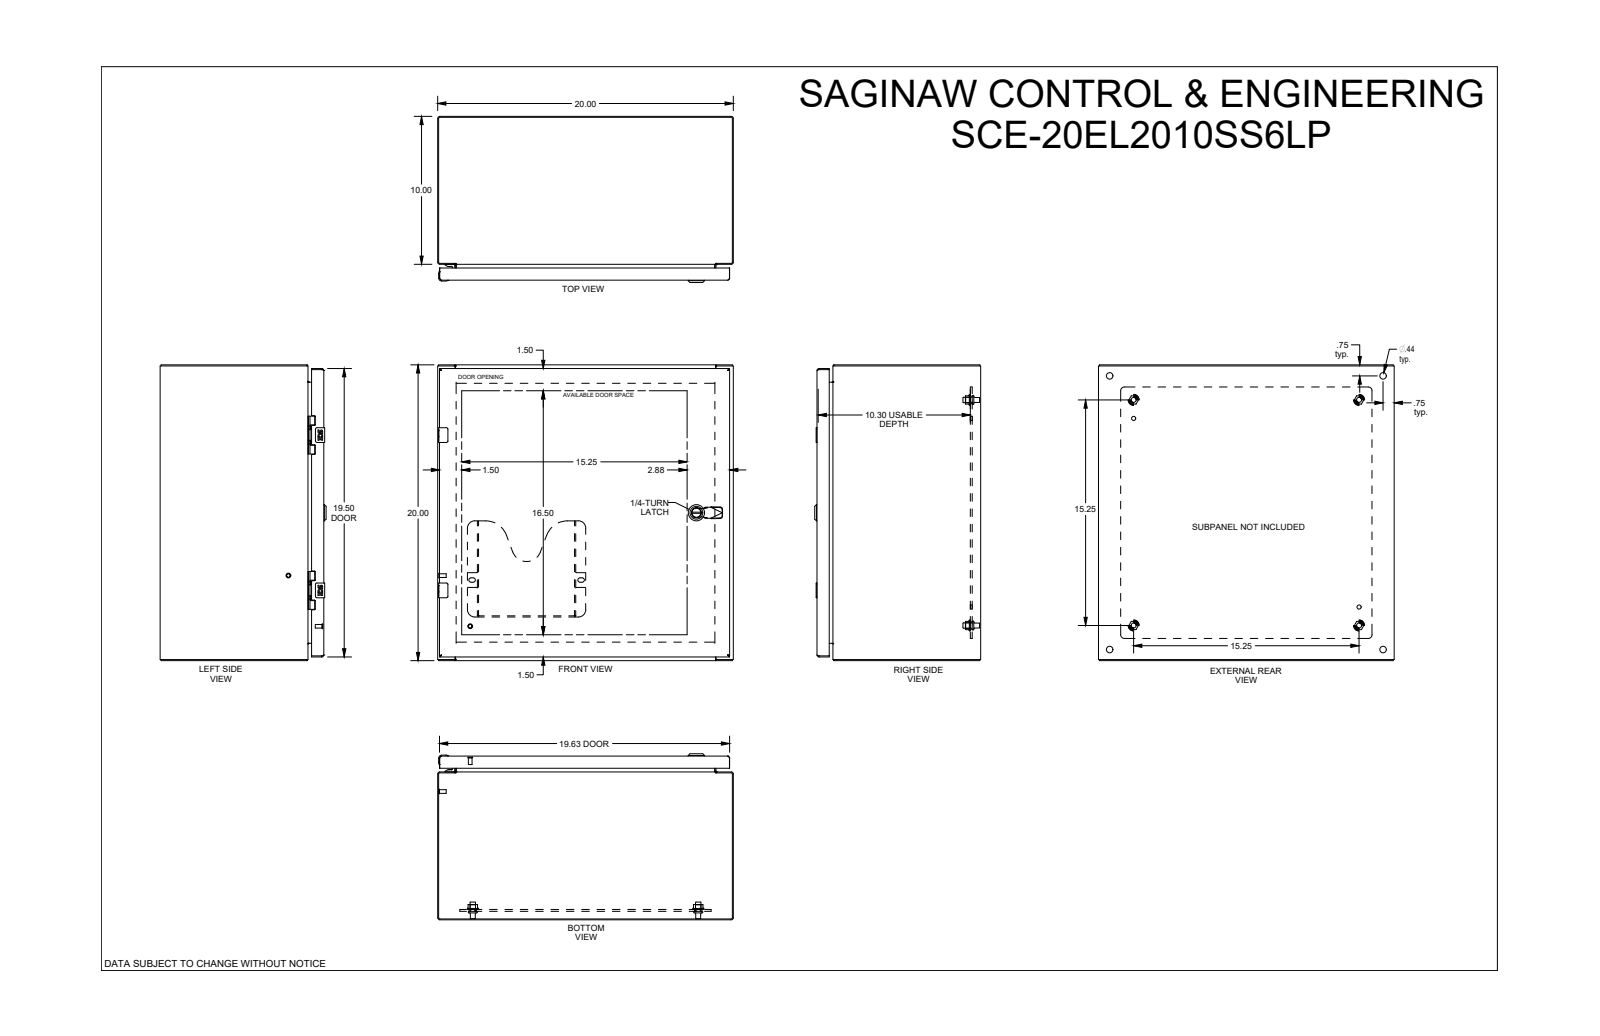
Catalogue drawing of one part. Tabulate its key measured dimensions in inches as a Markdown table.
| quantity | value |
| --- | --- |
| part name | SCE-20EL2010LP |
| STEP written by | SolidWorks 2021 (AUTOMOTIVE_DESIGN) |
| units | inches |
| bodies | 24 solids, 1217 faces (544 planar, 474 cylindrical, 199 other) |
| overall size | 20 × 20 × 11.935 |
| volume | 182.7 in³ |
| surface area | 4 462 in² |
| round holes (diameter × count) | 0.172 × 4, 0.205 × 4, 0.244 × 4, 0.375 × 4, 0.437 × 4, 0.5 × 4, 0.04 × 2, 0.188 × 2, 0.218 × 2, 0.281 × 2, 0.197 × 1, 0.204 × 1 |
| round bosses / shafts (diameter × count) | 0.375 × 4, 0.33 × 4, 0.25 × 4, 0.248 × 4, 0.24 × 4, 1.102 × 1, 0.78 × 1, 0.63 × 1 |
| partial cylindrical surfaces (radius × count) | 0.015 × 24, 0.04 × 17, 0.22 × 16, 0.043 × 12, 0.118 × 12, 0.031 × 10, 0.06 × 9, 0.062 × 8 |
| main face-to-face distances | 0.075, 19.925, 0.06, 10.993, 20, 19.85, 11.068, 11.008, 10.933, 0.125 |
| hole center spacings | 0.494, 10.5, 15.25, 0.984, 1.25, 2.332, 2.335, 2.452 |
